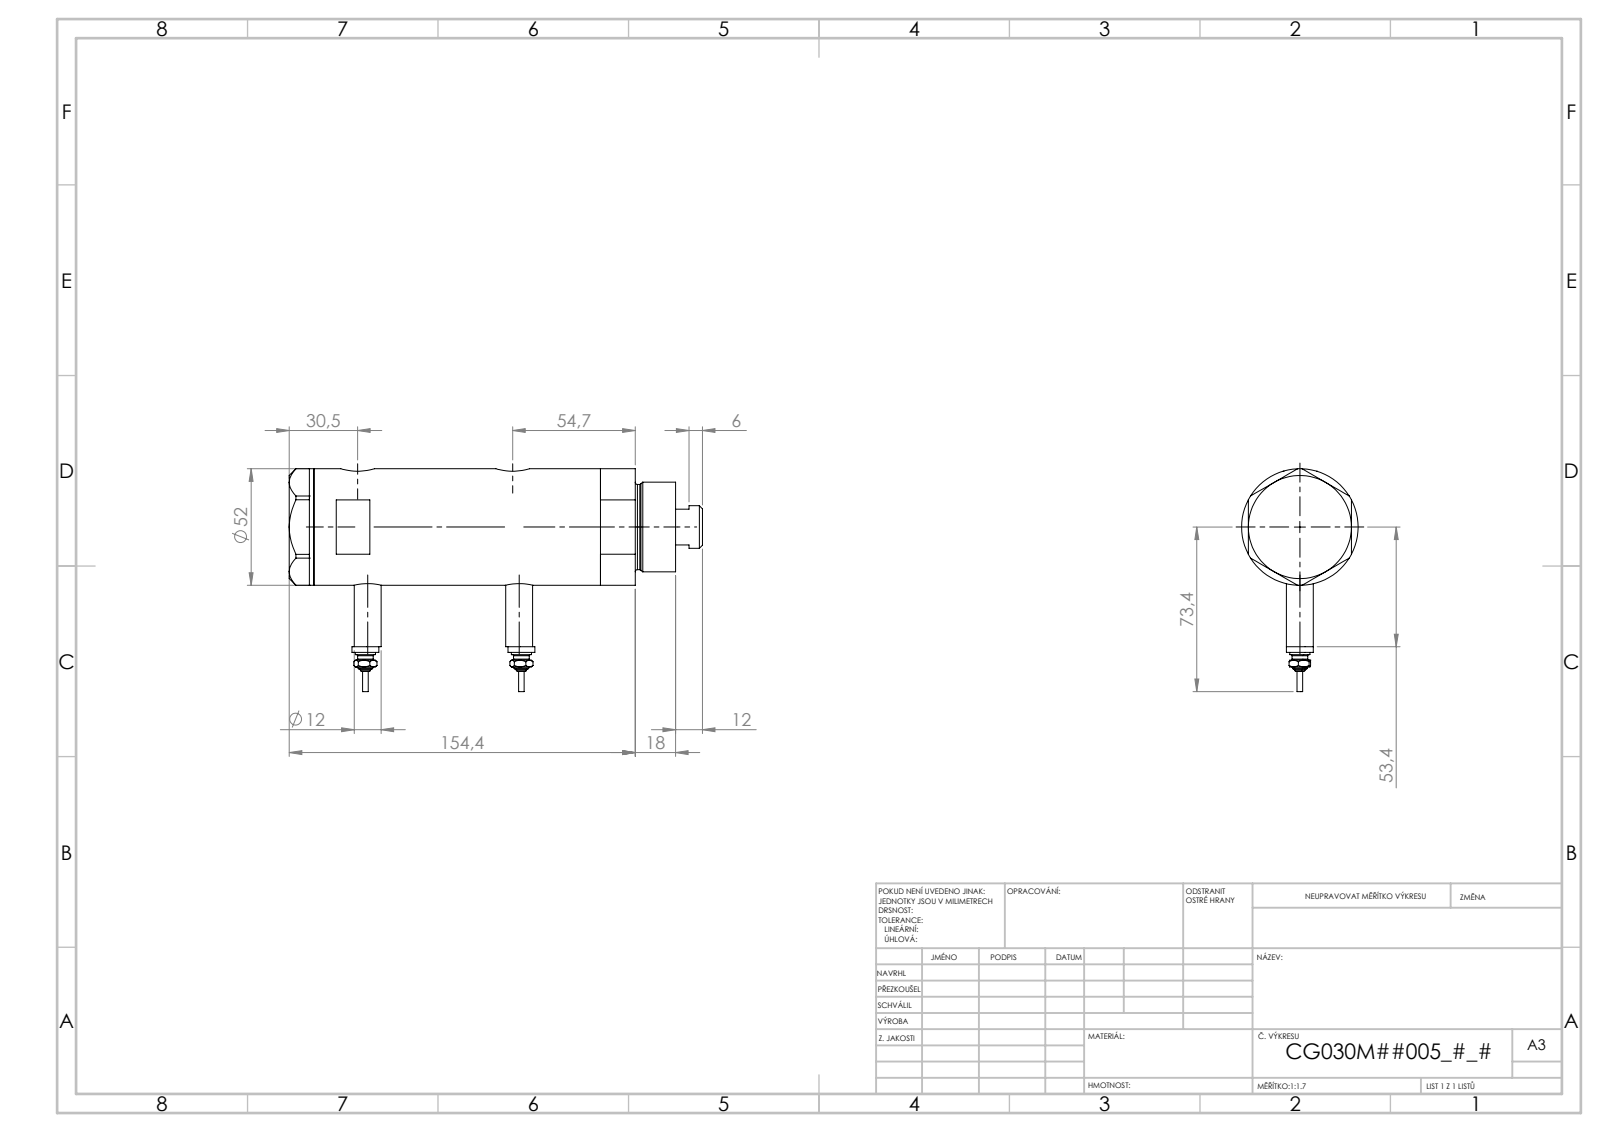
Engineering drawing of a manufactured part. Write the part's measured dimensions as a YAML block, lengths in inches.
part_name: "V270CG_MIDDLE; V270CG_BACK; V270CG_VC; V270CG_FRONT (+1 more)"
step_written_by: "SolidWorks 2019 (CONFIG_CONTROL_DESIGN)"
units: inches
bodies: {solids: 6, faces: 226, planar: 93, cylindrical: 69, other: 64}
overall_size: [7.26, 3.913, 2.047]
volume: 21.4
surface_area: 125.1
round_holes:
  - {diameter: 0.383, count: 2}
  - {diameter: 0.492, count: 2}
  - {diameter: 0.591, count: 2}
  - {diameter: 0.256, count: 1}
  - {diameter: 0.787, count: 1}
  - {diameter: 0.846, count: 1}
  - {diameter: 1.181, count: 1}
  - {diameter: 1.299, count: 1}
  - {diameter: 1.732, count: 1}
round_bosses_or_shafts:
  - {diameter: 0.472, count: 4}
  - {diameter: 0.354, count: 2}
  - {diameter: 0.276, count: 2}
  - {diameter: 0.177, count: 2}
  - {diameter: 0.098, count: 2}
  - {diameter: 2.047, count: 1}
  - {diameter: 1.575, count: 1}
  - {diameter: 1.496, count: 1}
face_to_face_distances: [3.602, 0.937, 2.665, 0.433, 1.37, 4.035, 1.811, 1.433, 5.469, 5.035]
hole_center_spacings: [0.114, 0.177, 2.547, 2.661, 2.724, 2.839]
